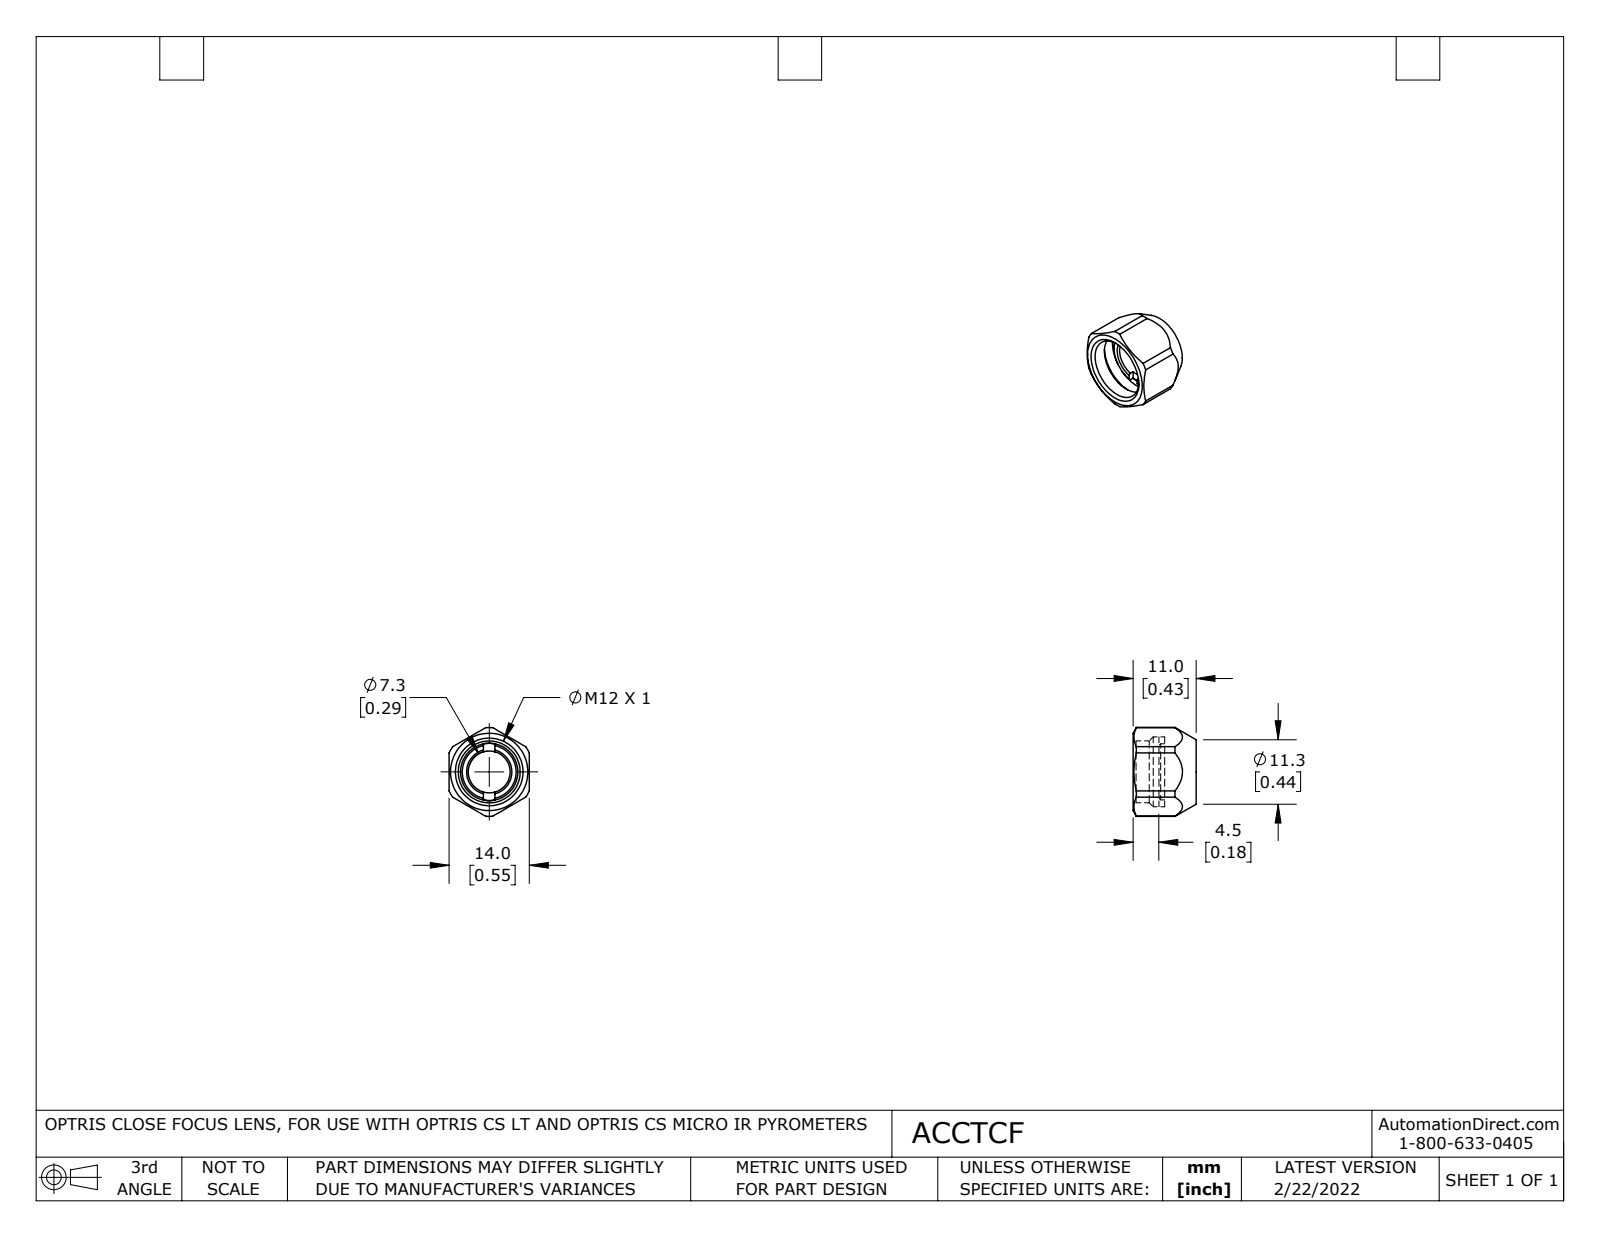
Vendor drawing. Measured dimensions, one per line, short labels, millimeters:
name: ACCTCF - CF-lens nc fxt
written by: SolidWorks 2021 (AUTOMOTIVE_DESIGN)
unit: mm
bodies: 3 solids, 78 faces (21 planar, 24 cylindrical, 33 other)
size: 15.5 × 14 × 11
volume: 1 000 mm³; area: 1 428 mm²
holes: 1× ⌀7.3, 1× ⌀8.1, 1× ⌀9.4, 1× ⌀10.1, 1× ⌀10.8, 1× ⌀12.2
bosses: 1× ⌀10, 1× ⌀8
rounds: 1× R7.7
face distances: 14, 5.5, 3.3, 2.2, 11, 8.8, 8, 3, 0.8, 2.5
